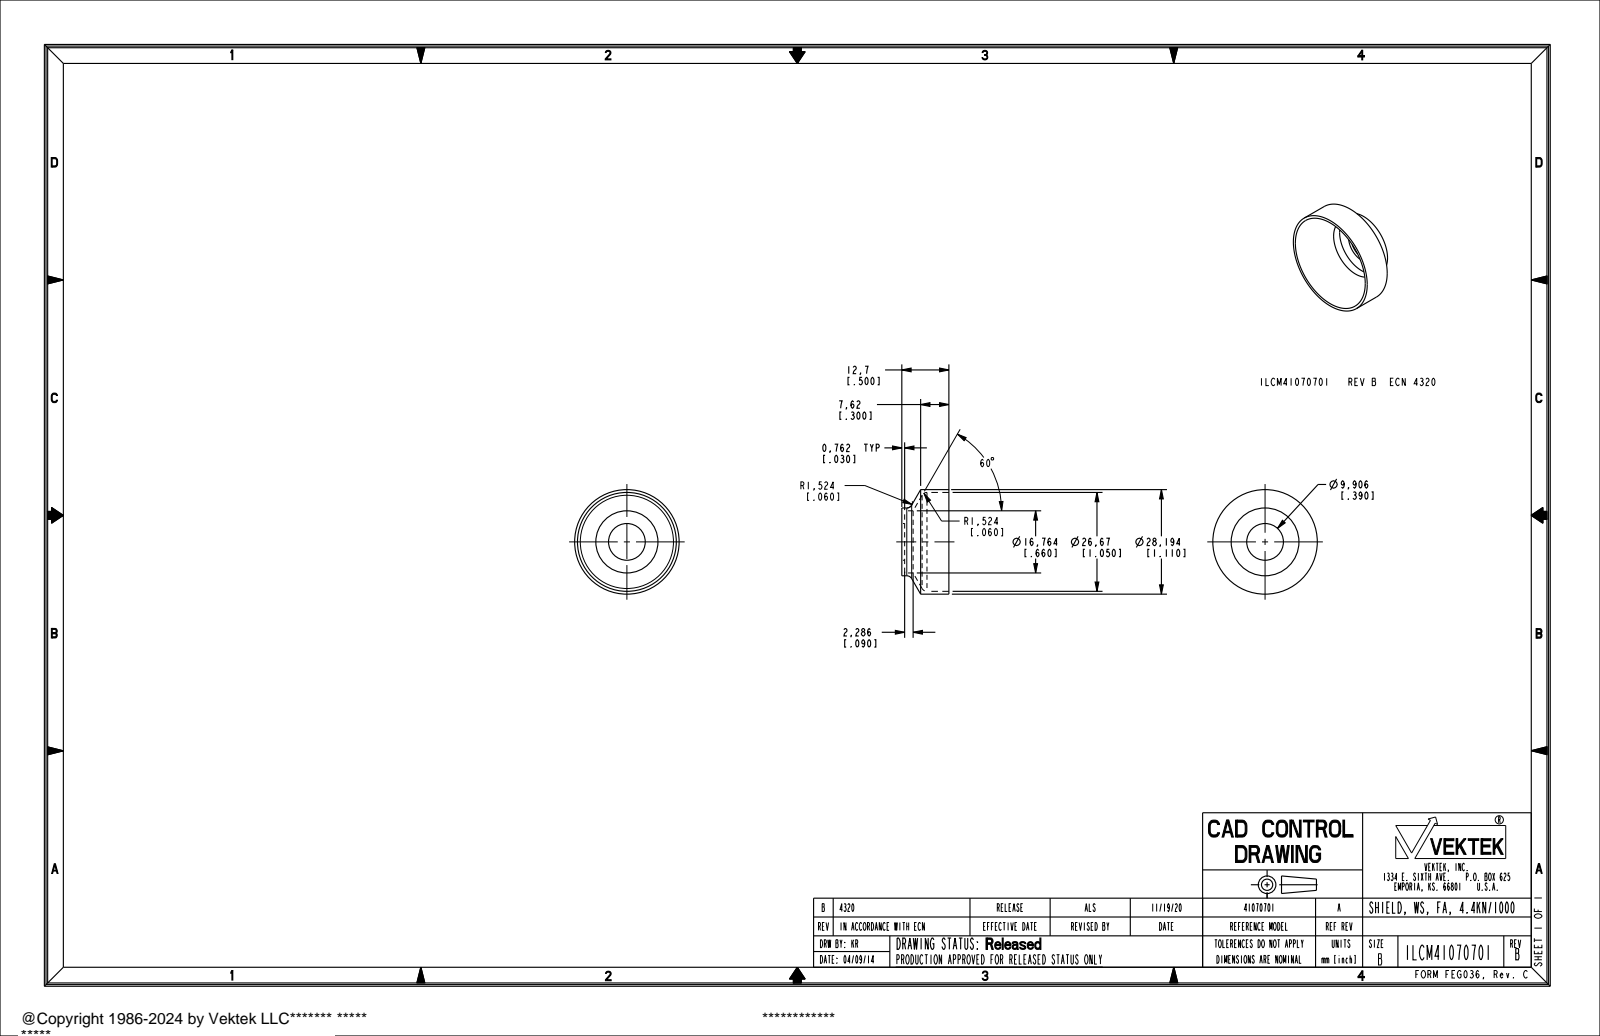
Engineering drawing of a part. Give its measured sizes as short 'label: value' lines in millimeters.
name: ILCM41070701
written by: PRO/ENGINEER BY PARAMETRIC TECHNOLOGY CORPORATION, 2013320 (CONFIG_CONTROL_DESIGN)
unit: mm
bodies: 1 solid, 21 faces (3 planar, 10 cylindrical, 8 other)
size: 28.19 × 28.19 × 12.7
volume: 1 154 mm³; area: 2 695 mm²
holes: 1× ⌀9.91, 1× ⌀16.76, 1× ⌀26.67
bosses: 1× ⌀28.19, 1× ⌀18.29
face distances: 0.76, 12.7, 11.94
